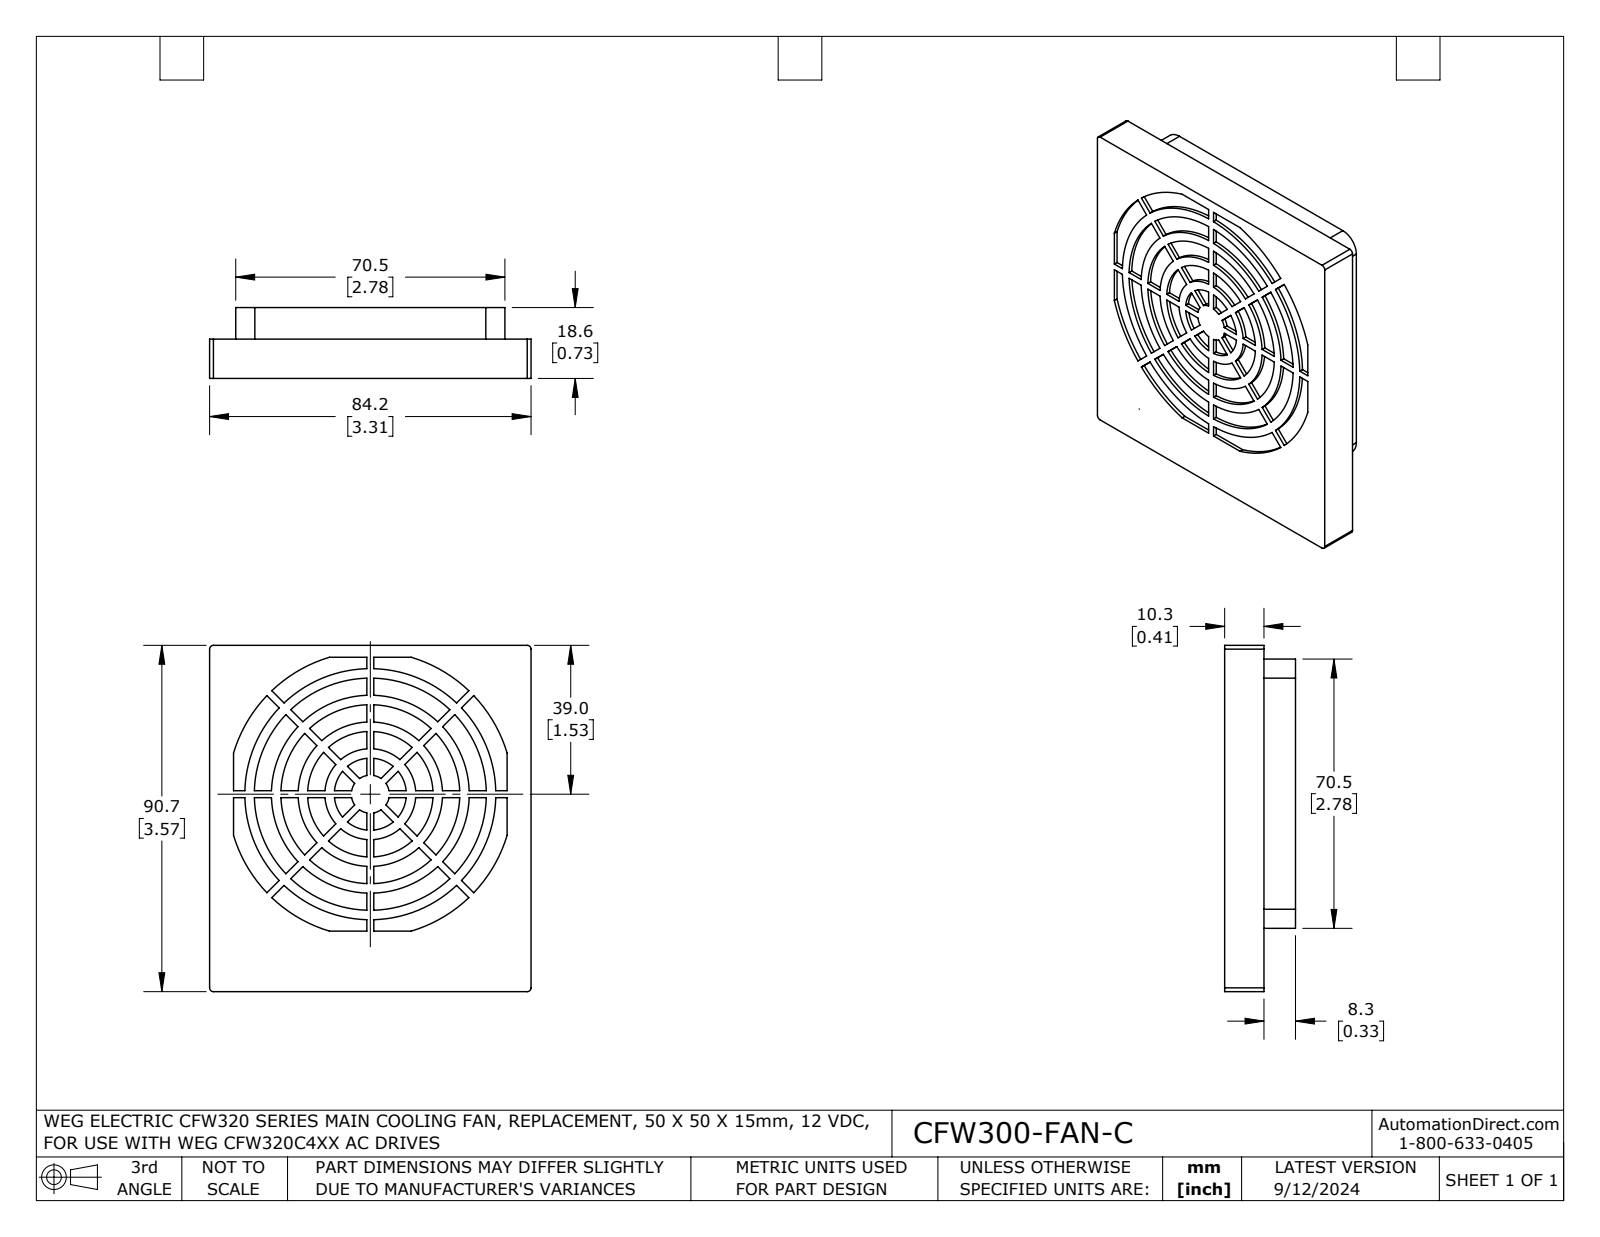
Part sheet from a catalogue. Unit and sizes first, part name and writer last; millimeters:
Units: millimetres
Overall size (bounding box): 90.7 × 84.2 × 18.6
Round holes (diameter × count): ⌀32.9 ×1, ⌀46.9 ×1, ⌀60.8 ×1
Round bosses / shafts (diameter × count): ⌀65.8 ×1, ⌀51.8 ×1, ⌀37.8 ×1, ⌀23.8 ×1
Partial cylindrical surfaces — rounded edges, fillets, slot ends (radius × count): R1 ×4, R5 ×4, R5 ×1, R9.4 ×1, R15 ×1, R36 ×1, R37.4 ×1
Main face-to-face distances: 17.6, 1, 7.3, 10.3, 16.6, 9.3, 8.3, 18.6, 6.9, 77.3
Volume: 113 900 mm³ · Surface area: 23 140 mm²
Bodies: 1 solid, 256 faces (155 planar, 101 cylindrical, 0 other)
Part name (STEP PRODUCT): CFW300-FAN-C
STEP written by: SolidWorks 2021 (AUTOMOTIVE_DESIGN)
